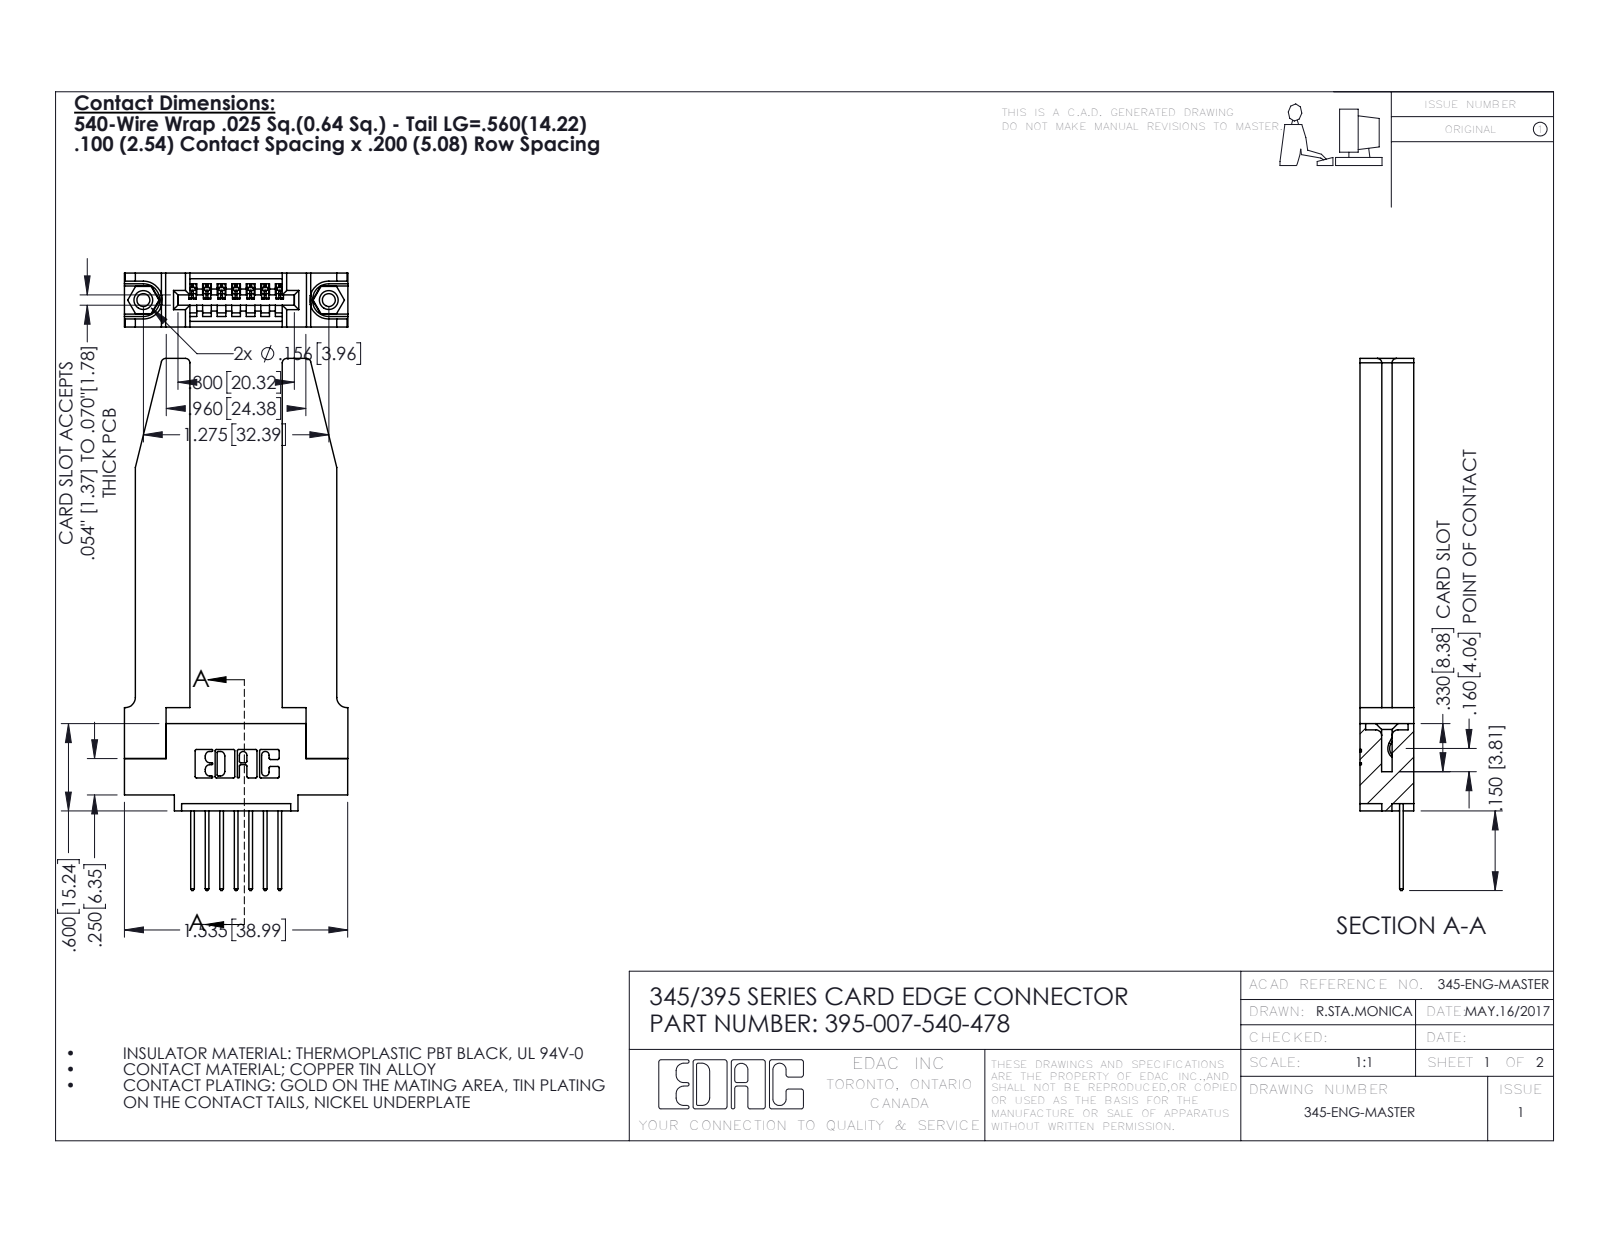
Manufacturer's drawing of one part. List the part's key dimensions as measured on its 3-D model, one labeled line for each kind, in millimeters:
Part name (STEP PRODUCT): 345 Part_0.110 Offset - 0.156 Dia-TH; 395-007-540-478; 345-292-001_345-293-140; 345-220-078_345-220-078 (+1 more)
STEP written by: SolidWorks 2016 (CONFIG_CONTROL_DESIGN)
Units: millimetres
Bodies: 12 solids, 770 faces (506 planar, 212 cylindrical, 52 other)
Overall size (bounding box): 92.9 × 39 × 9.4
Volume: 11 100 mm³ · Surface area: 10 980 mm²
Round holes (diameter × count): ⌀2.3 ×2, ⌀3.2 ×2, ⌀4 ×2, ⌀1.6 ×1
Round bosses / shafts (diameter × count): ⌀3.9 ×2
Partial cylindrical surfaces — rounded edges, fillets, slot ends (radius × count): R0.3 ×22, R0.2 ×14, R0.3 ×14, R0.8 ×8, R0.2 ×6, R0.8 ×6, R0.7 ×3, R0.8 ×2
Main face-to-face distances: 9.4, 3.8, 1.8, 5.6, 7.6, 3.8, 16.1, 2, 5.1, 1.8
Hole centre spacings: 6.9, 26.5, 32.4
